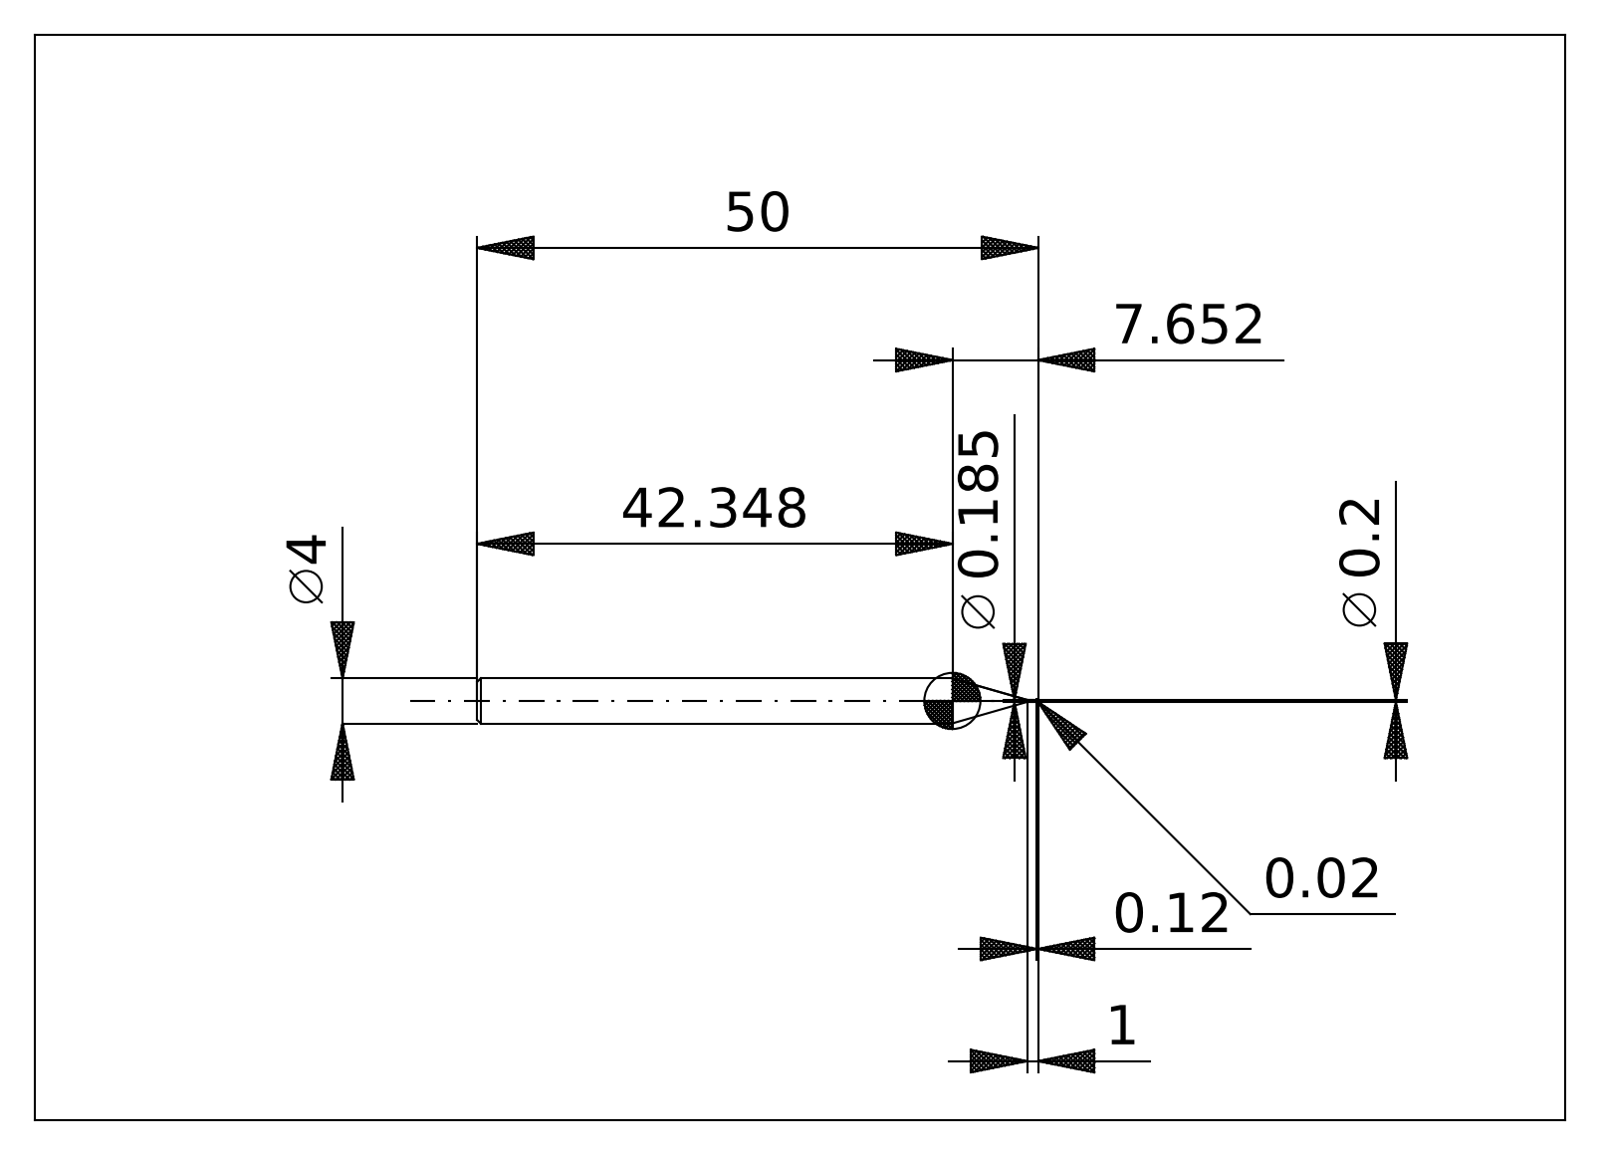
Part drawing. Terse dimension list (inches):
written by: ACIS (automotive_design)
unit: in
bodies: 2 solids, 26 faces (6 planar, 8 cylindrical, 12 other)
size: 1.969 × 0.157 × 0.157
volume: 0.034 in³; area: 0.913 in²
bosses: 1× ⌀0.157
face distances: 1.969, 1.967, 1.964, 0.301, 0.3, 0.296, 1.667
